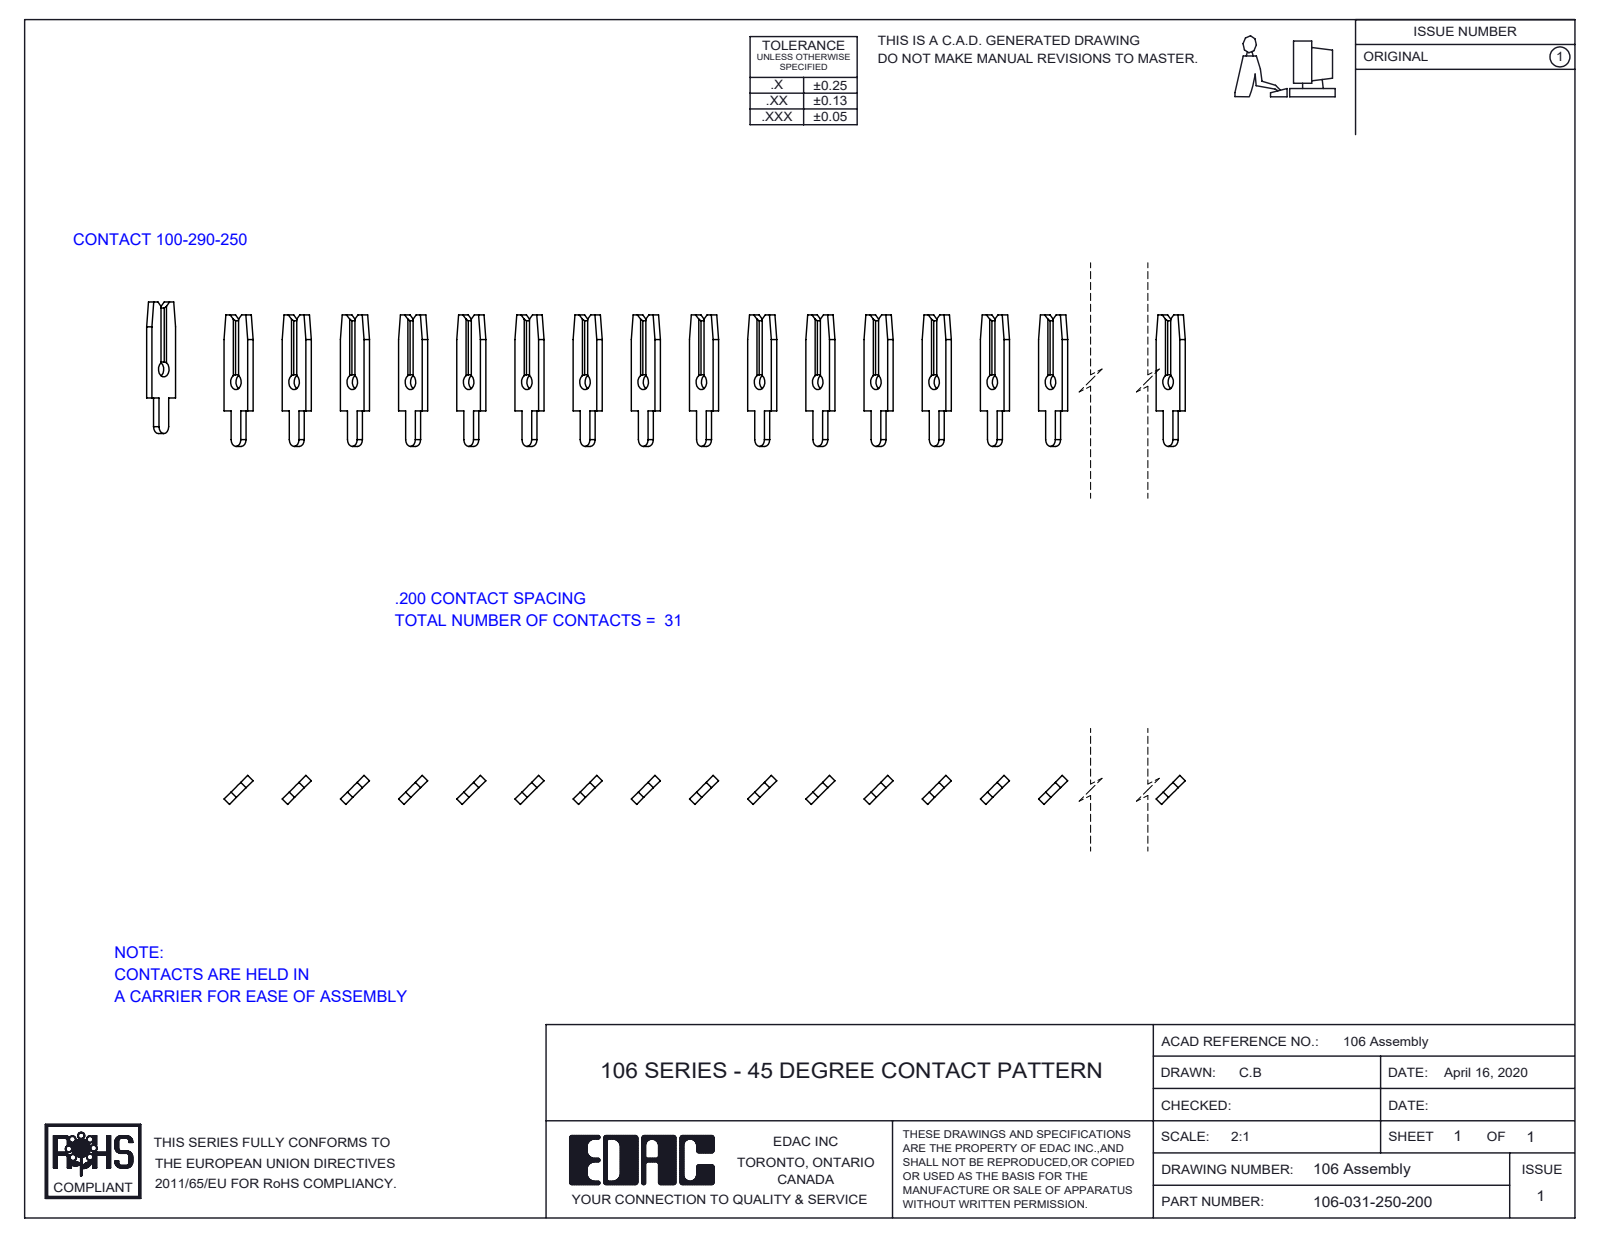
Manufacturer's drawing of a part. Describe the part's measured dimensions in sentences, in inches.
The part is named "100-290-001_100-290-250; 106-031-250-200". Its 3-D file was written by "SolidWorks 2016 (CONFIG_CONTROL_DESIGN)". It is 31 solids with 744 faces: 620 planar, 124 cylindrical and 0 other. Overall it measures 6.1 by 0.452 by 0.1 inches. Its volume is 0.03 cubic inches and its surface area 3.524 square inches. Round holes: 31 of diameter 0.052. Partial cylindrical surfaces (rounded edges, fillets, slot ends): 31 of radius 0.024. The main face-to-face distances are 0.141, 0.848, 0.707, 0.283, 0.99, 0.566, 0.424, 1.131, 0.424, 1.556. The hole center spacings are 0.141, 0.283, 0.424, 0.848, 1.839, 0.99, 1.556, 1.697.
